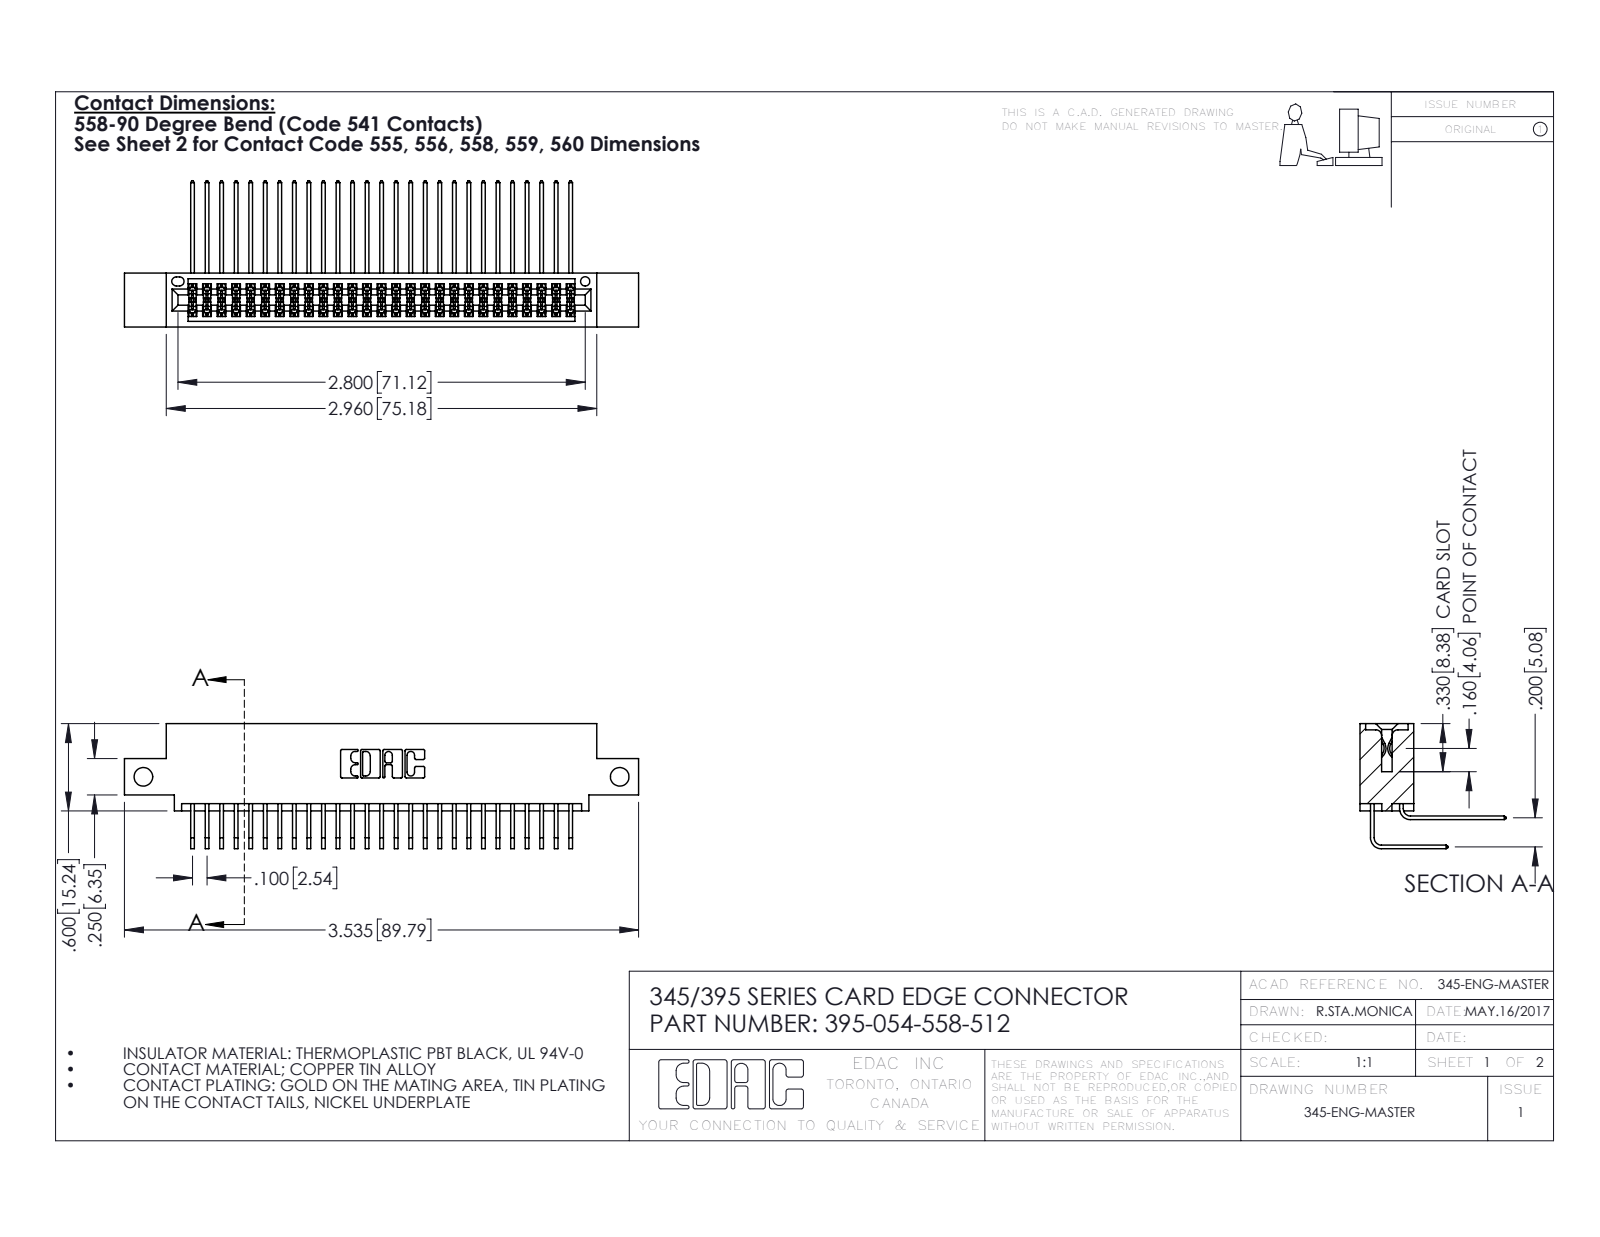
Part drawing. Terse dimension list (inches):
name: 395-054-558-512; 345-292-001_558 Tail - 2; 345-292-001_558 559 Tail - 1; 345 Part_0.110 Offset - Side Mount
written by: SolidWorks 2016 (CONFIG_CONTROL_DESIGN)
unit: in
bodies: 55 solids, 2938 faces (1974 planar, 964 cylindrical, 0 other)
size: 3.535 × 1.005 × 0.859
volume: 0.533 in³; area: 21.76 in²
holes: 2× ⌀0.128, 1× ⌀0.064
rounds: 82× R0.006, 22× R0.01, 6× R0.007, 6× R0.031, 3× R0.026, 2× R0.014, 2× R0.019, 2× R0.022
face distances: 0.072, 0.298, 0.2, 0.37, 0.098, 0.272, 0.025, 0.225, 0.025, 0.175
hole spacings: 3.275
